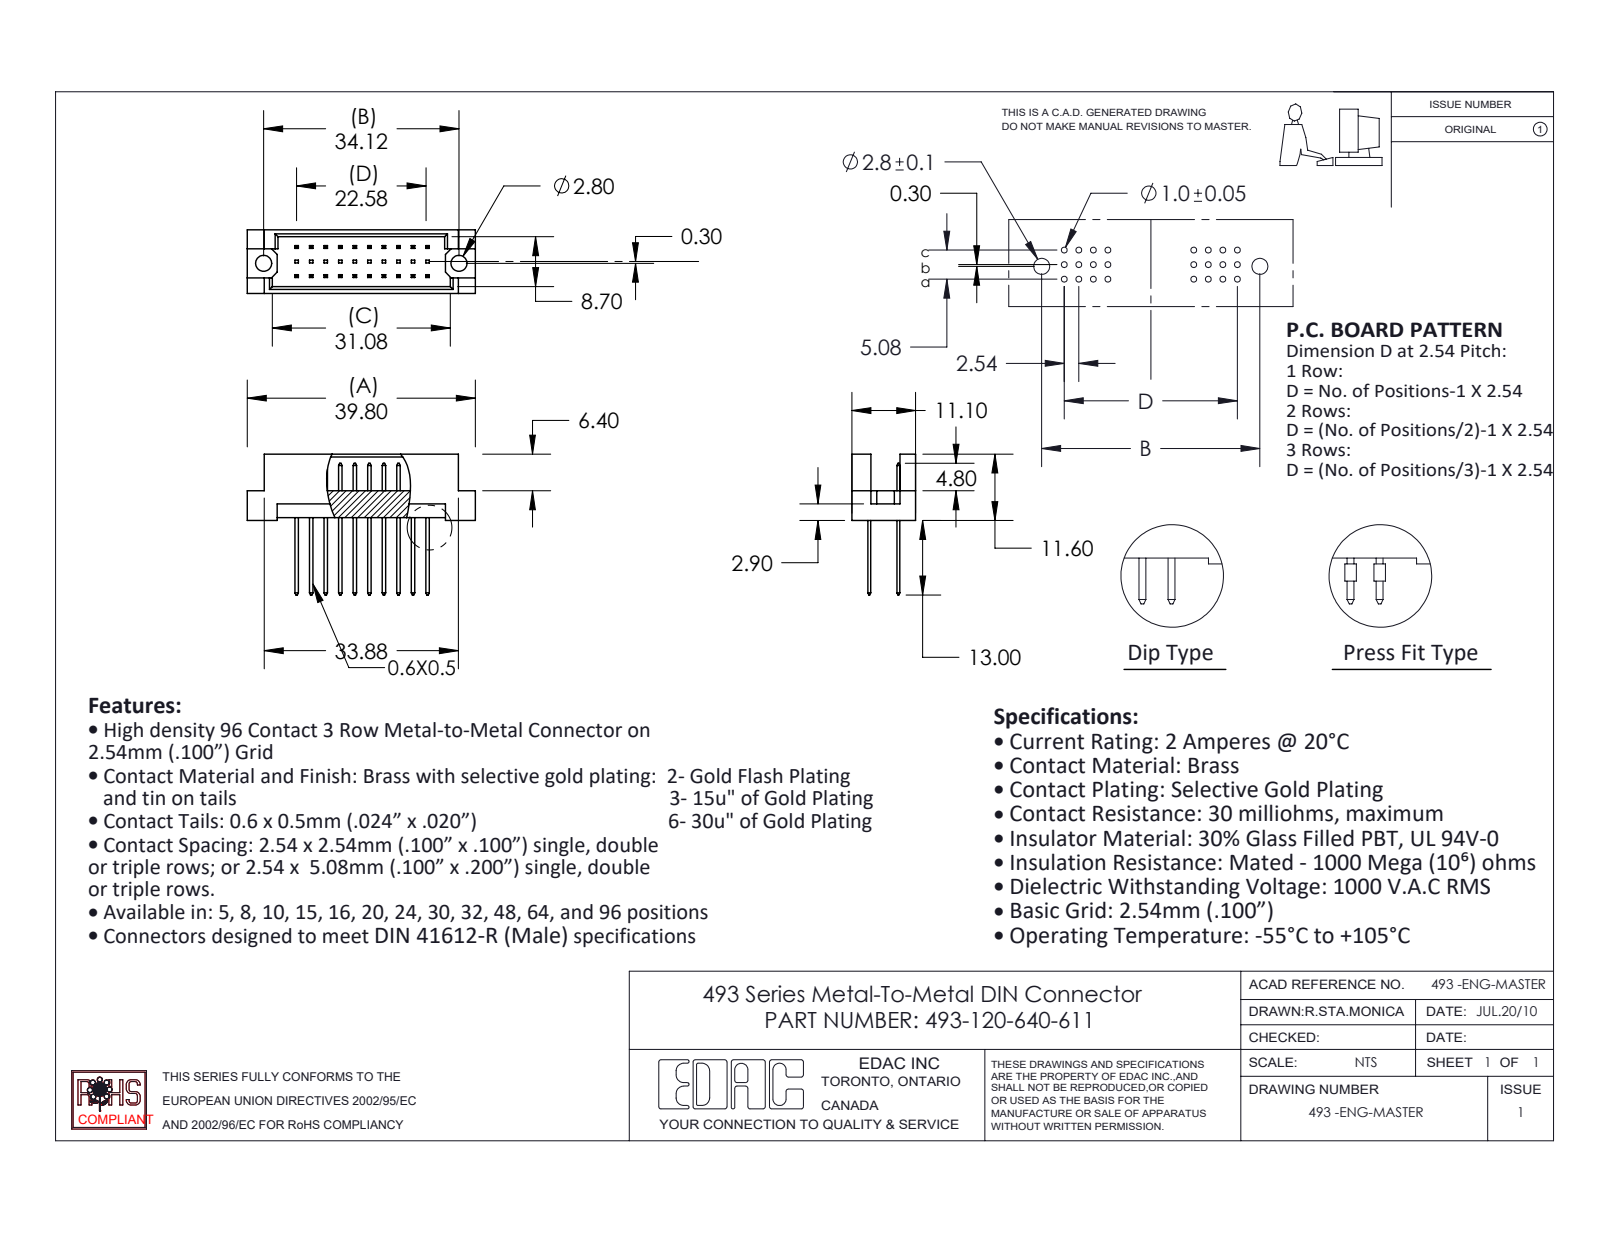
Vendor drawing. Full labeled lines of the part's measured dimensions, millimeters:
Part name (STEP PRODUCT): 493-290_40; 493 Part_30; 493-120-640-611
STEP written by: SolidWorks 2020 (CONFIG_CONTROL_DESIGN)
Units: millimetres
Bodies: 21 solids, 452 faces (448 planar, 4 cylindrical, 0 other)
Overall size (bounding box): 39.8 × 24.6 × 11.1
Volume: 2 509 mm³ · Surface area: 3 742 mm²
Round holes (diameter × count): ⌀2.8 ×2
Main face-to-face distances: 5.08, 2.54, 1.2, 9.9, 0.5, 11.1, 2.76, 3.26, 7.84, 8.34
Hole centre spacings: 34.12
